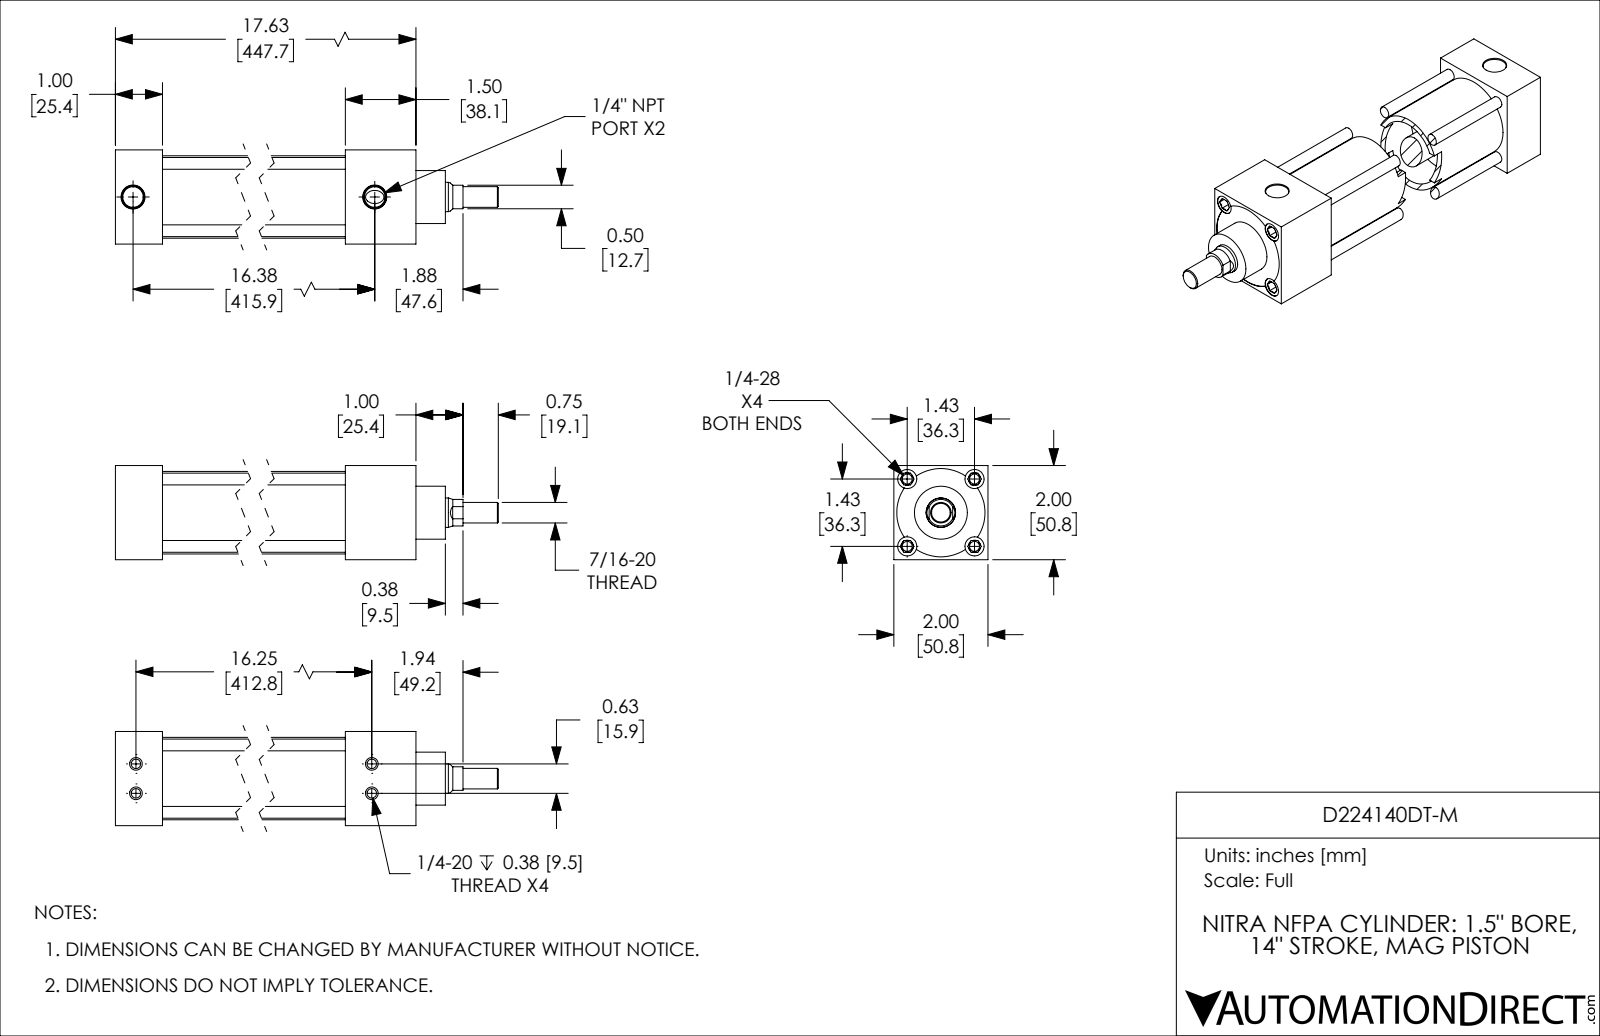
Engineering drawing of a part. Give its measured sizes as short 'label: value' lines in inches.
name: D224140DT-M; D224140DT-M_BODY; D224140DT-M_PISTON_KK1
written by: SolidWorks 2019 (CONFIG_CONTROL_DESIGN)
unit: in
bodies: 2 solids, 203 faces (58 planar, 65 cylindrical, 80 other)
size: 19.375 × 2 × 2
volume: 29.15 in³; area: 291.7 in²
holes: 4× ⌀0.201, 4× ⌀0.213, 4× ⌀0.406, 2× ⌀0.438, 1× ⌀0.626, 1× ⌀1.501
bosses: 4× ⌀0.25, 1× ⌀1.751, 1× ⌀1.499, 1× ⌀1.125, 1× ⌀0.624, 1× ⌀0.437
rounds: 1× R0.281, 1× R0.937
face distances: 2, 1, 16.125, 15.125, 17.62, 16.62, 1.495, 1.125, 2.125, 14
hole spacings: 0.319, 1.011, 1.43, 0.625, 2.022, 16.25, 16.262, 16.315
